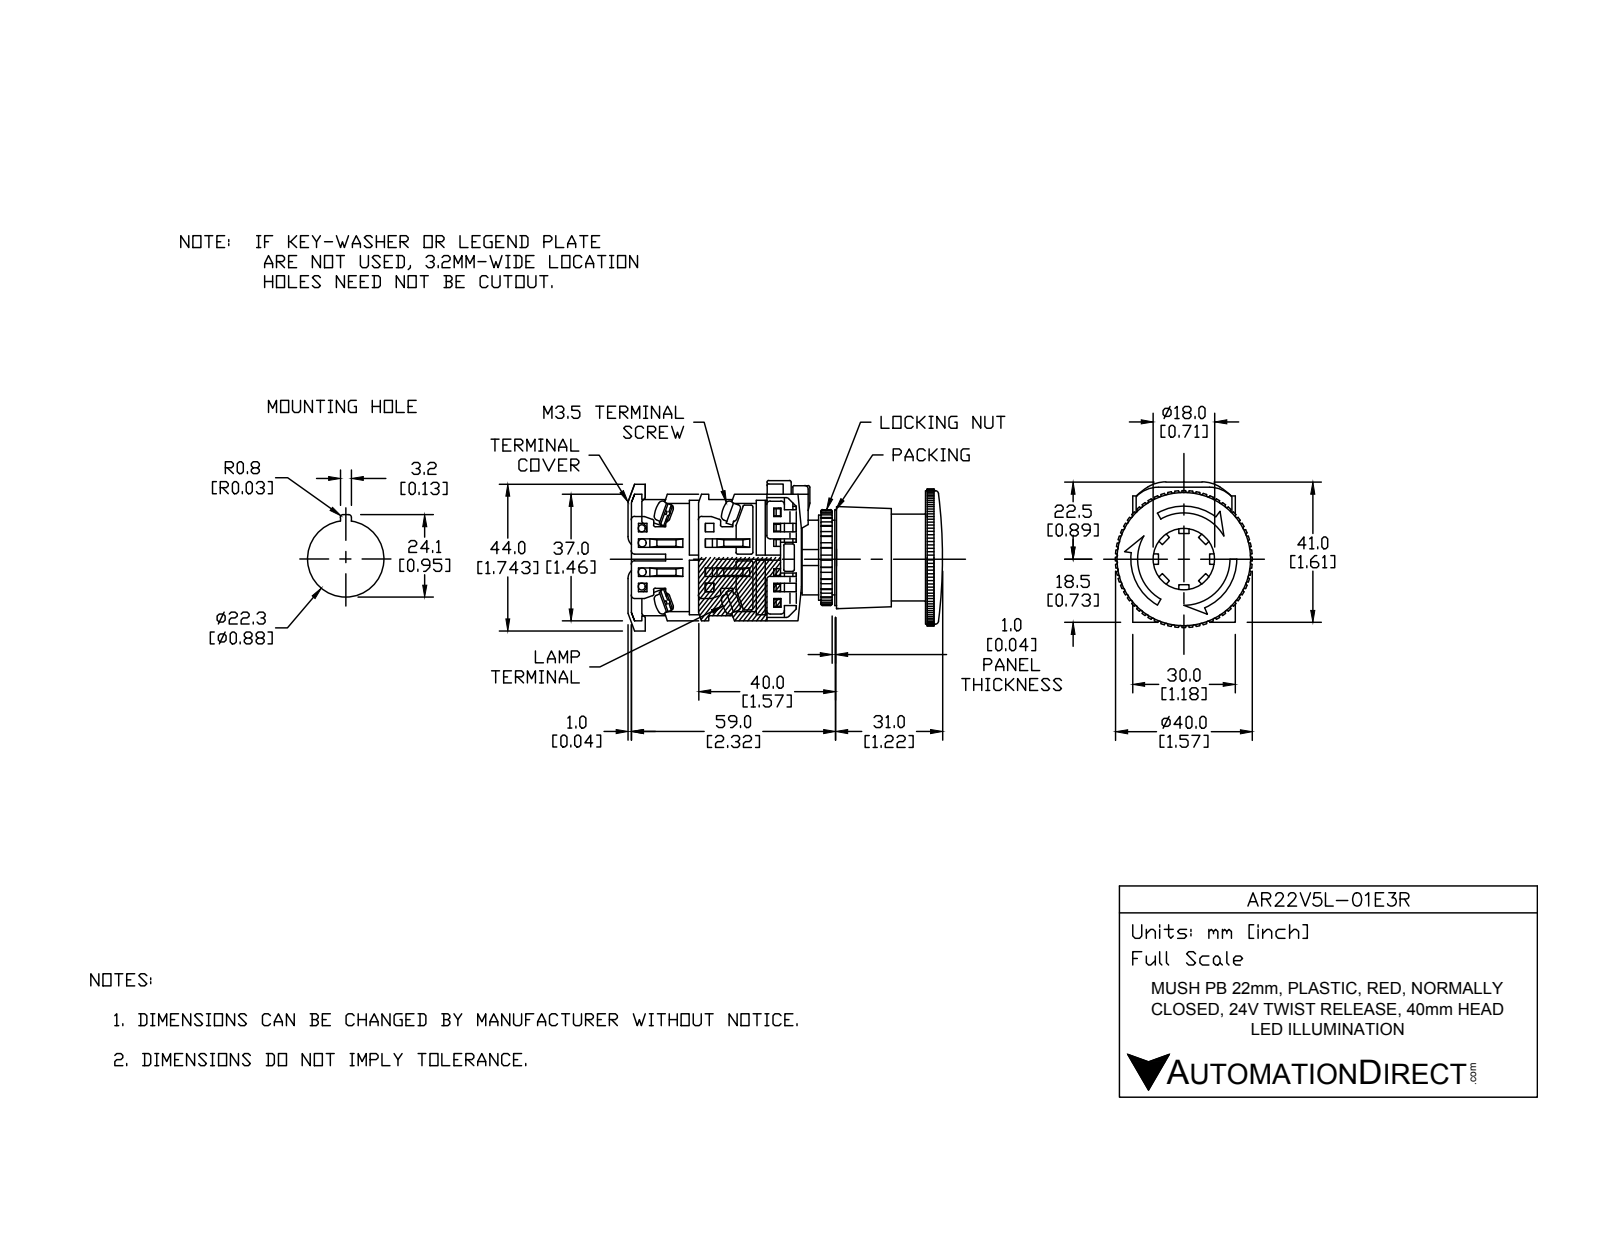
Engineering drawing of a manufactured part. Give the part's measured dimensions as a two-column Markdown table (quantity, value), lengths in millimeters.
| quantity | value |
| --- | --- |
| part name | AR22V5L-01E3R |
| STEP written by | SolidWorks 2017 (AUTOMOTIVE_DESIGN) |
| units | millimeters |
| bodies | 18 solids, 733 faces (310 planar, 314 cylindrical, 109 other) |
| overall size | 72.5 × 43.81 × 39.99 |
| volume | 45 765 mm³ |
| surface area | 26 751 mm² |
| round holes (diameter × count) | 14.8 × 1, 21.8 × 1, 22 × 1, 25.4 × 1 |
| round bosses / shafts (diameter × count) | 5 × 4, 29.8 × 1, 25 × 1, 24 × 1, 21.75 × 1, 17 × 1, 14.5 × 1 |
| partial cylindrical surfaces (radius × count) | 0.5 × 119, 1.75 × 8, 5 × 4, 4 × 2, 13.5 × 1, 15 × 1, 16.59 × 1, 17.59 × 1 |
| main face-to-face distances | 1, 29, 10, 18, 2, 20.5, 20, 16, 30.5, 22.5 |
